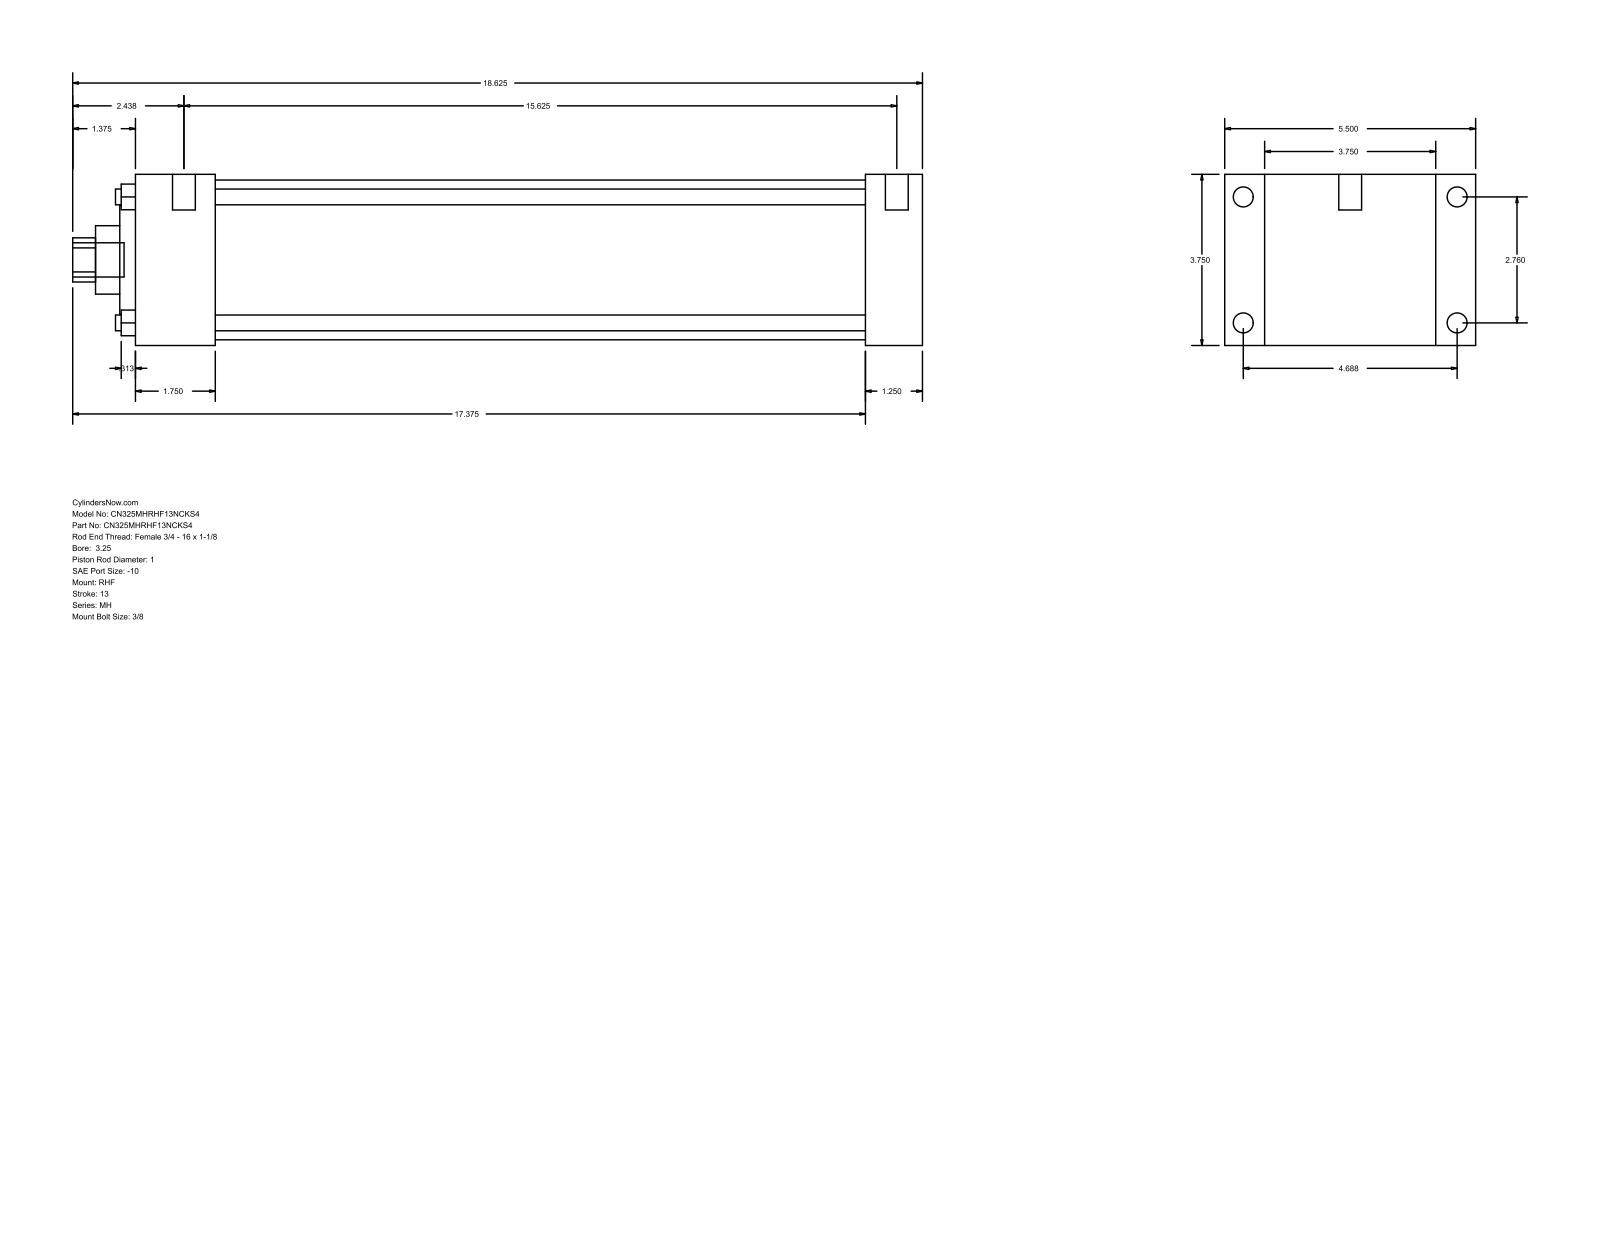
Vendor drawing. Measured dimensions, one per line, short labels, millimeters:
name: MH_RHF__0325_1
written by: GSSL Pune (CONFIG_CONTROL_DESIGN)
unit: mm
bodies: 0 solids, 90 faces (61 planar, 29 cylindrical, 0 other)
size: 473.07 × 139.7 × 95.25
holes: 4× ⌀8.76, 1× ⌀25.4, 1× ⌀38.1, 1× ⌀60.33, 1× ⌀88.9
bosses: 4× ⌀11.13, 4× ⌀5.56, 2× ⌀12.7, 1× ⌀19.05
rounds: 1× R12.29
face distances: 95.24, 31.75, 22.23, 117.47, 406.4, 438.15, 139.7, 44.46, 361.94, 393.69
hole spacings: 49.57, 70.1, 99.14
